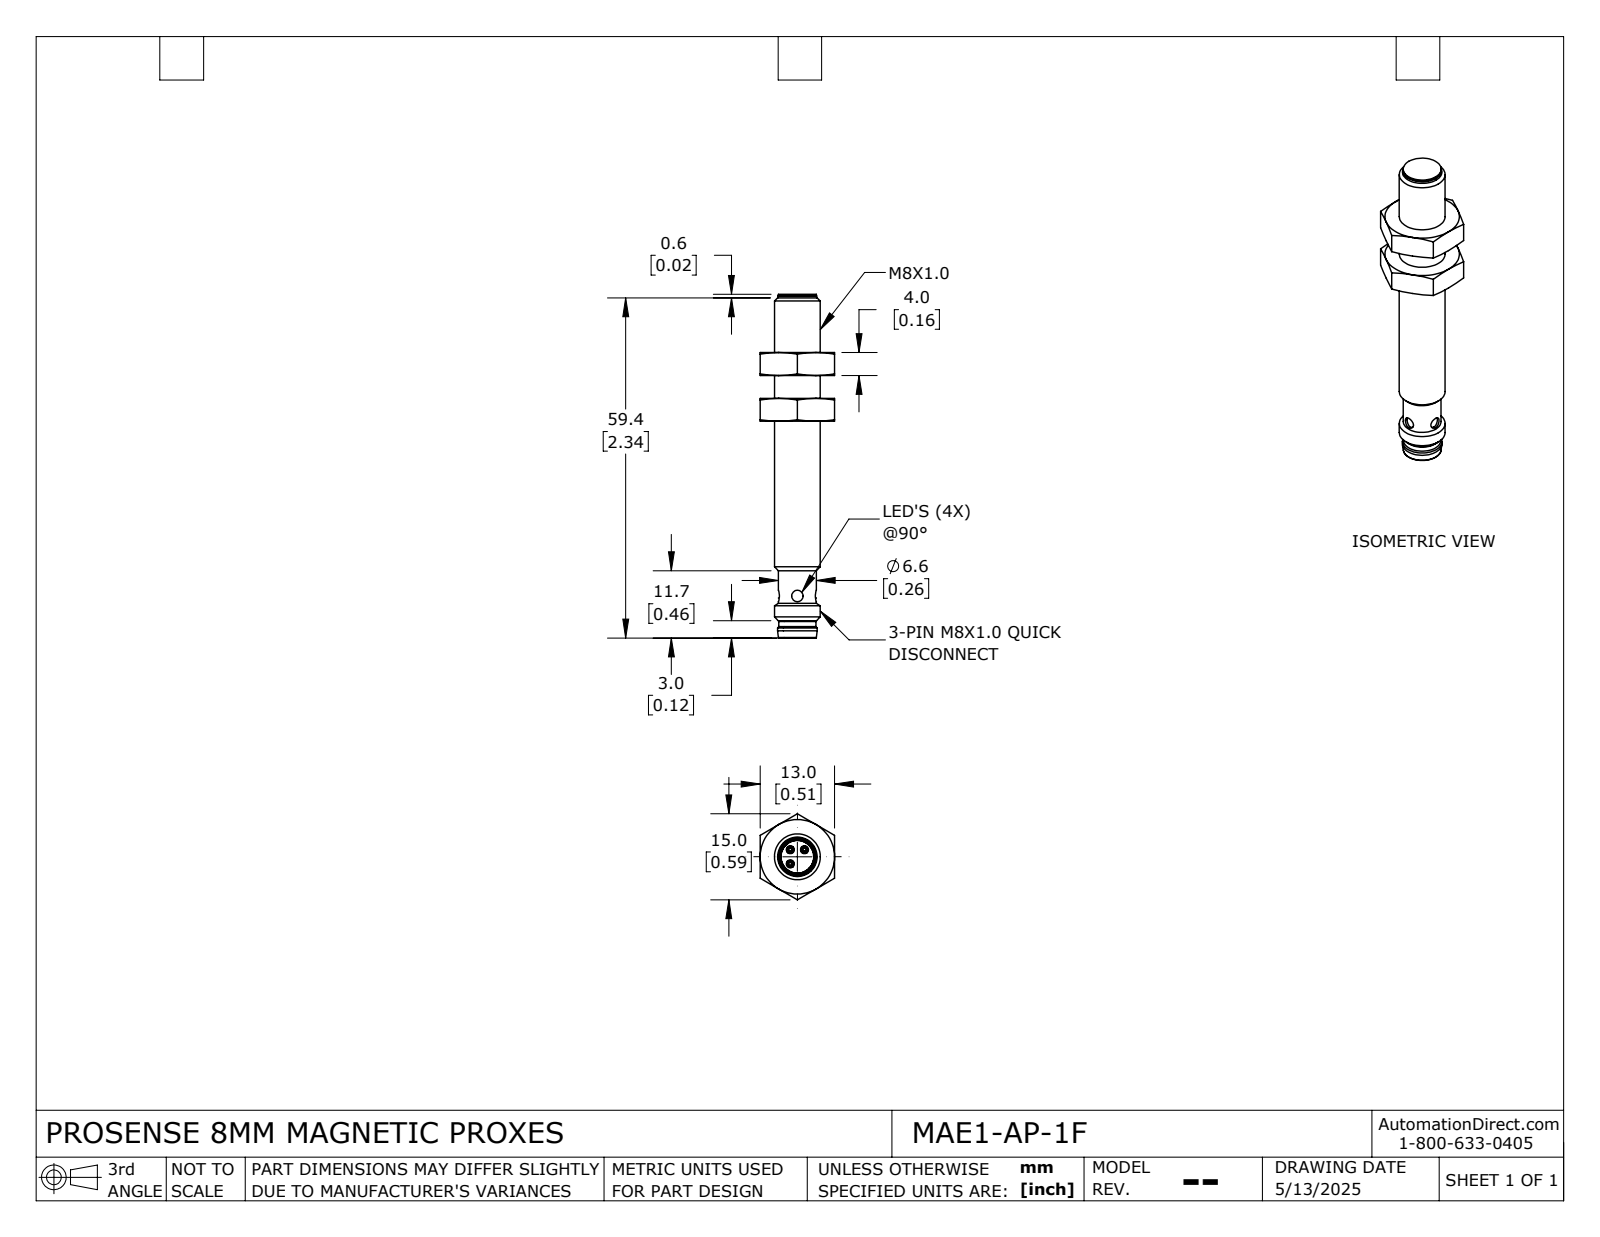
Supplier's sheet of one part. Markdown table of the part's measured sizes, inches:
| quantity | value |
| --- | --- |
| part name | ME5021Z01 |
| STEP written by | SolidWorks 2024 (AUTOMOTIVE_DESIGN) |
| units | inches |
| bodies | 8 solids, 285 faces (67 planar, 108 cylindrical, 110 other) |
| overall size | 2.362 × 0.591 × 0.512 |
| volume | 0.133 in³ |
| surface area | 6.255 in² |
| round holes (diameter × count) | 0.041 × 3, 0.043 × 3, 0.079 × 2, 0.193 × 1, 0.228 × 1, 0.23 × 1, 0.253 × 1, 0.272 × 1 |
| round bosses / shafts (diameter × count) | 0.039 × 3, 0.315 × 1, 0.272 × 1, 0.263 × 1, 0.261 × 1, 0.26 × 1, 0.256 × 1, 0.25 × 1 |
| partial cylindrical surfaces (radius × count) | 0.012 × 18, 0.004 × 5, 0.019 × 3, 0.037 × 3, 0.008 × 2, 0.014 × 1, 0.102 × 1 |
| main face-to-face distances | 0.157, 0.512, 0.315, 0.472, 0.392, 0.55, 0.707, 0.865, 0.4, 0.557 |
| hole center spacings | 0.069, 0.097, 0.098, 0.138 |
